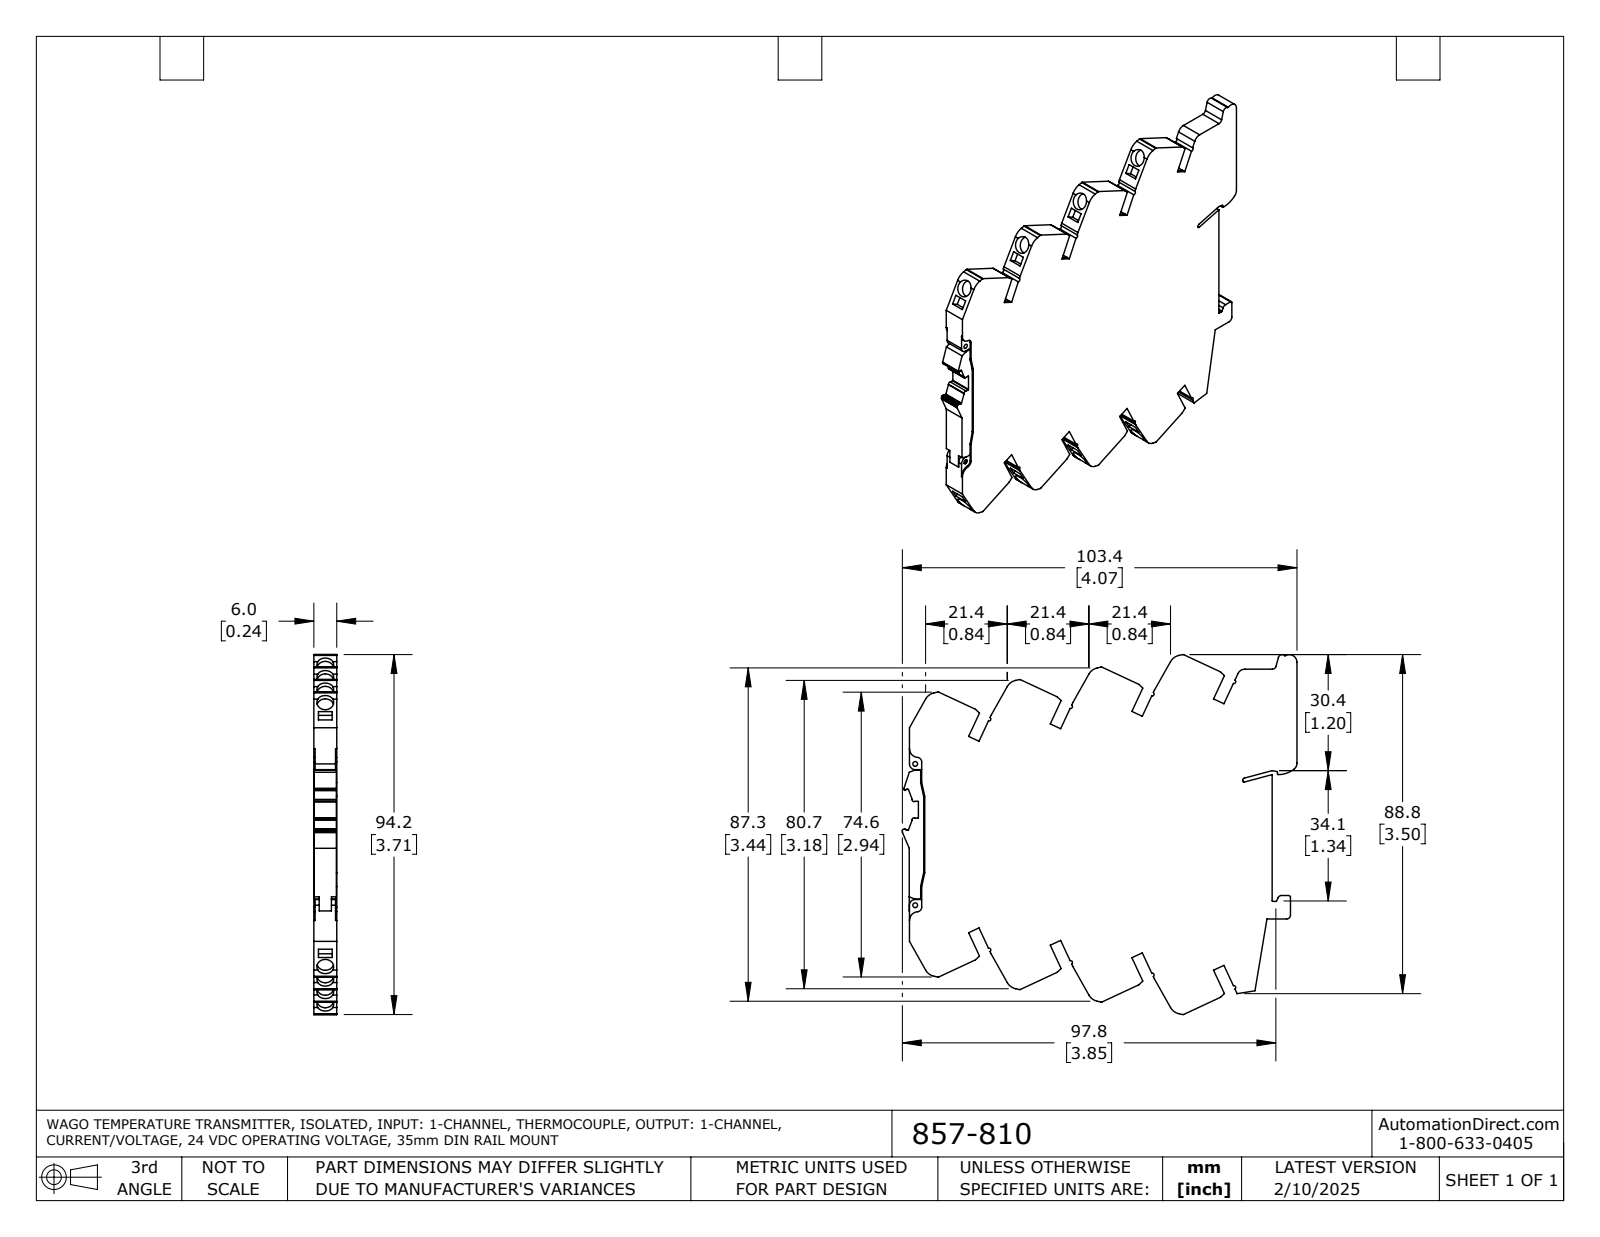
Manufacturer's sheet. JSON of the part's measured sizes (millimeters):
{"part_name": "857-810", "step_written_by": "SolidWorks 2021 (AUTOMOTIVE_DESIGN)", "units": "millimeters", "bodies": {"solids": 1, "faces": 317, "planar": 219, "cylindrical": 98, "other": 0}, "overall_size": [103.4, 94.3, 6], "volume_mm3": 43930, "surface_area_mm2": 19260, "round_holes": [[4.4, 8], [1.2, 2]], "partial_cylinders_radius": [[0.5, 12], [0.2, 11], [0.4, 8], [3.4, 8], [1, 4], [0.3, 3], [2, 3], [0.5, 2]], "face_to_face_distances": [6, 18, 17, 12, 5.9, 12, 3, 24, 36, 6.5], "hole_center_spacings": [13.4, 13.3, 26.7, 26.7, 26.7, 37, 40, 40.1]}
